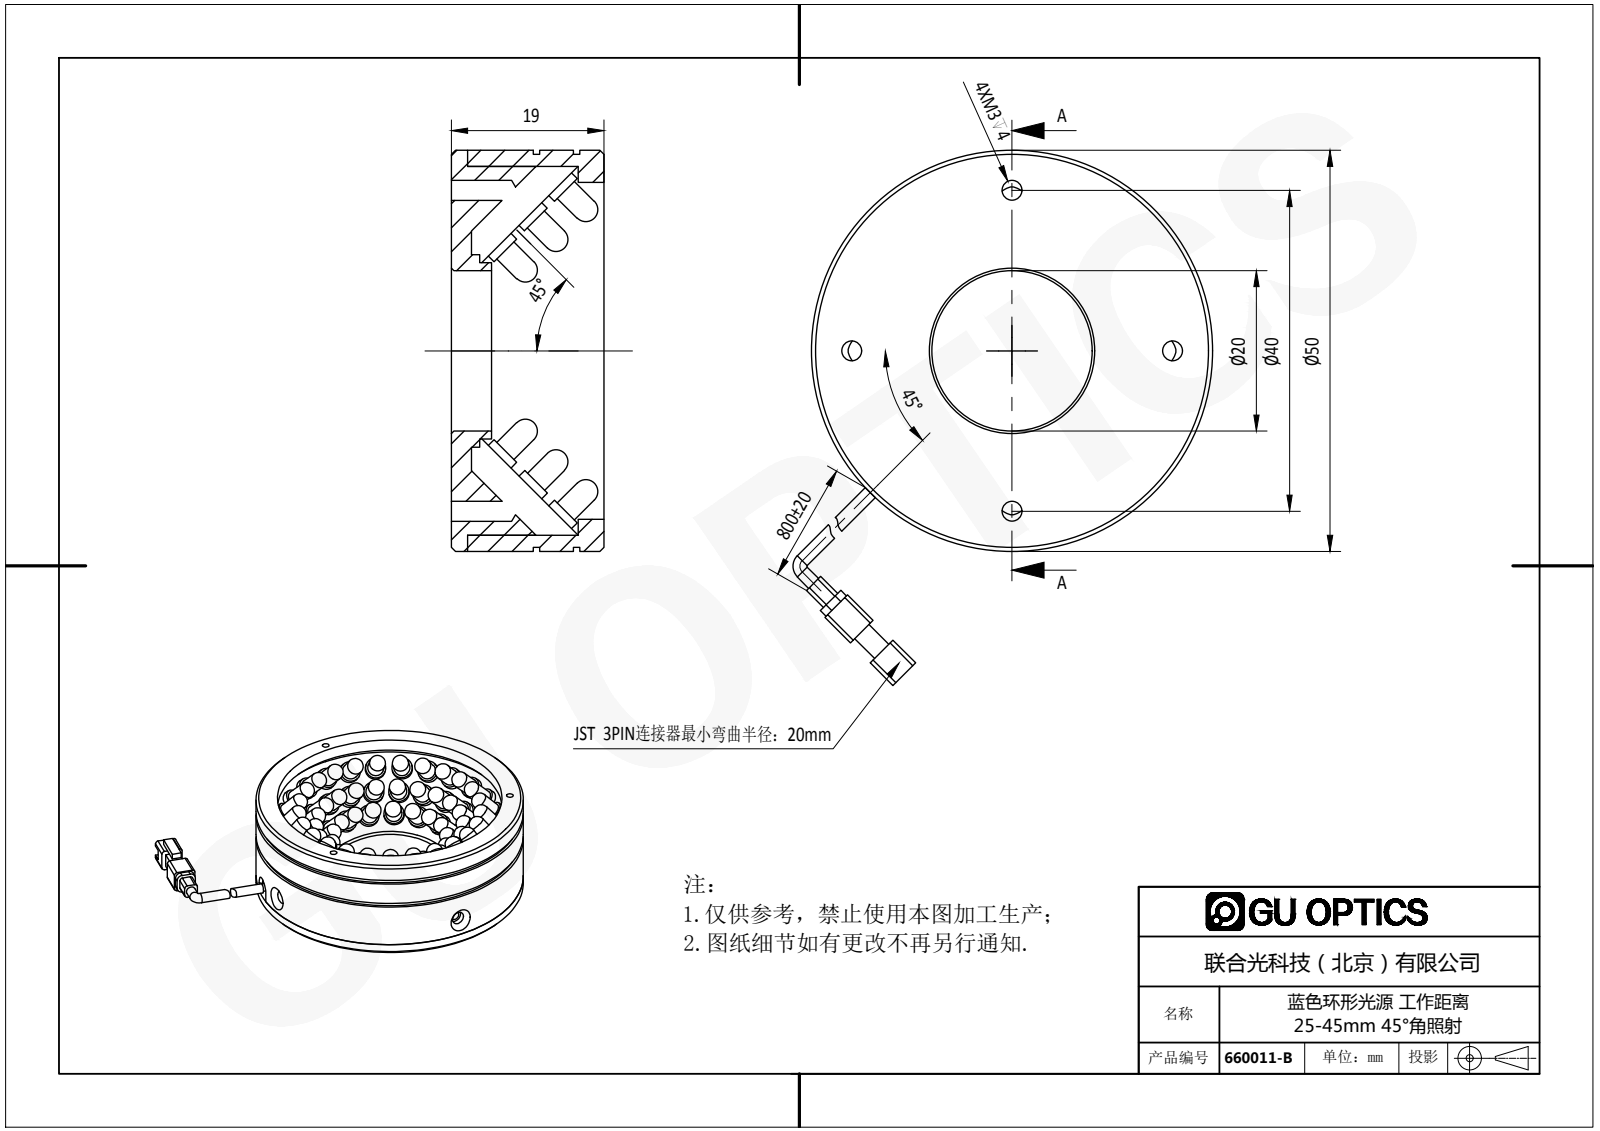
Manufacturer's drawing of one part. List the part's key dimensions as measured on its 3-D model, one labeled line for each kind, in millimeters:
Part name (STEP PRODUCT): 660011-B
STEP written by: SolidWorks 2016 (AUTOMOTIVE_DESIGN)
Units: millimetres
Bodies: 70 solids, 1331 faces (857 planar, 361 cylindrical, 113 other)
Overall size (bounding box): 66.72 × 52.33 × 19
Volume: 17 436 mm³ · Surface area: 21 875 mm²
Round holes (diameter × count): ⌀2.5 ×4, ⌀1.25 ×3, ⌀3 ×3, ⌀1.6 ×2, ⌀2.4 ×2, ⌀20 ×1, ⌀42 ×1
Round bosses / shafts (diameter × count): ⌀3.8 ×65, ⌀3 ×63, ⌀1.75 ×2, ⌀50 ×1, ⌀49 ×1, ⌀46 ×1, ⌀24 ×1, ⌀22 ×1
Partial cylindrical surfaces — rounded edges, fillets, slot ends (radius × count): R0.5 ×10, R1 ×4, R1.6 ×1, R4.5 ×1
Main face-to-face distances: 2, 0.5, 19, 17, 2.5, 1, 3, 16.5, 5, 0.8
Hole centre spacings: 20, 28.28, 22.5, 38.97, 11.26, 30.1, 40, 2.5
